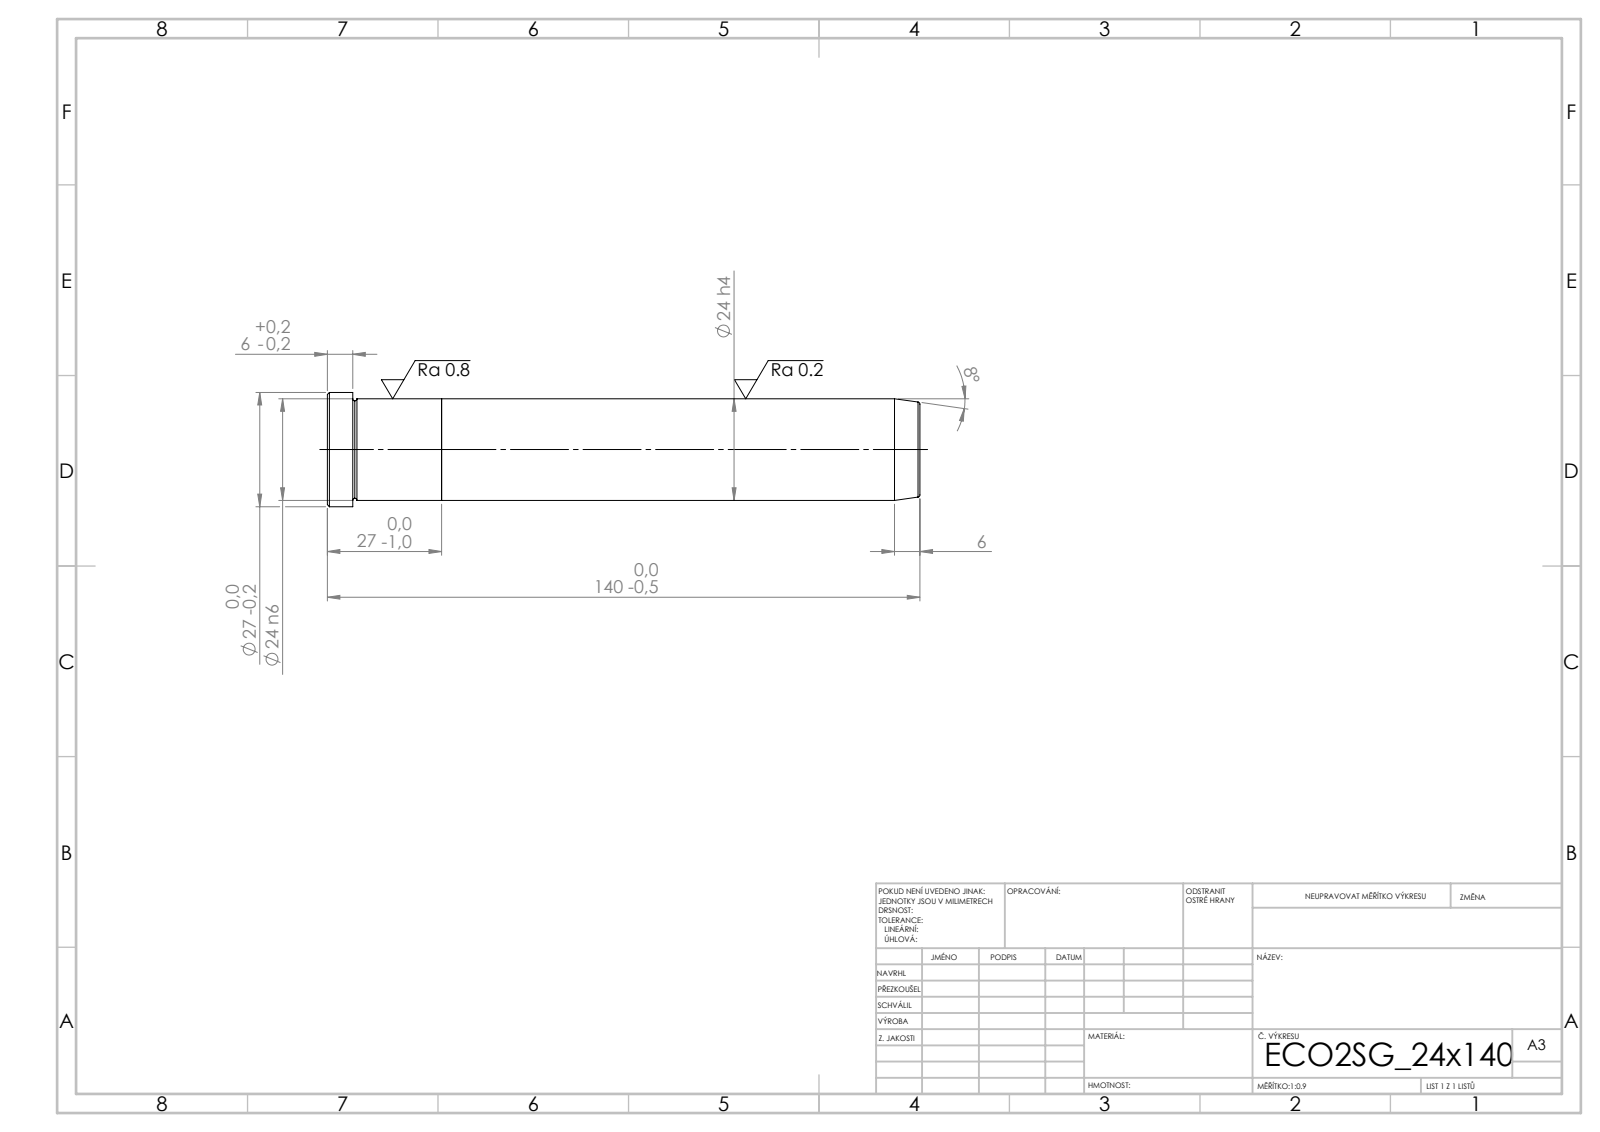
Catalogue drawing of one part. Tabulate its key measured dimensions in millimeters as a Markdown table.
| quantity | value |
| --- | --- |
| STEP written by | SolidWorks 2019 (CONFIG_CONTROL_DESIGN) |
| units | millimeters |
| bodies | 2 solids, 21 faces (5 planar, 6 cylindrical, 10 other) |
| overall size | 140 × 27 × 27 |
| volume | 63 827 mm³ |
| surface area | 12 593 mm² |
| round bosses / shafts (diameter × count) | 27 × 1, 24 × 1 |
| main face-to-face distances | 27, 113, 140, 134, 21, 6 |
